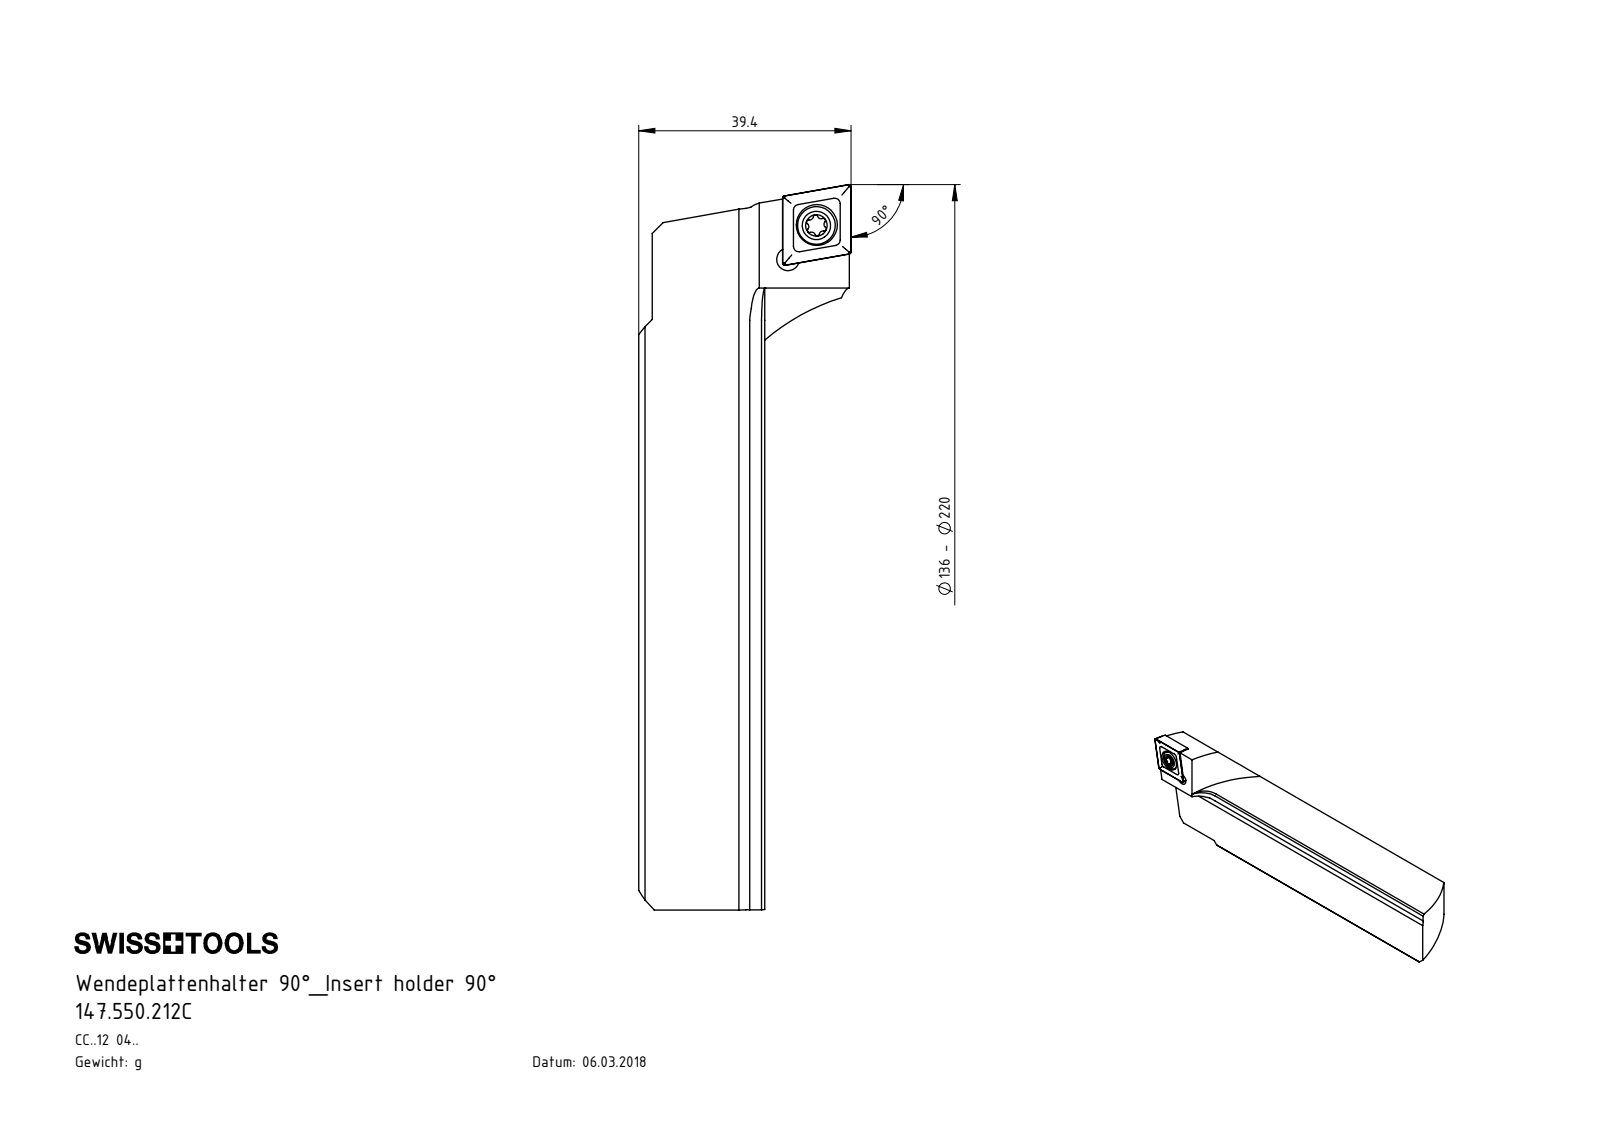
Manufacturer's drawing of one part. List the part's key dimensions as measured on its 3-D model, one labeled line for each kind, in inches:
Part name (STEP PRODUCT): F00-WCC.136.001_C; WCC-ER2.001.010_A; CCMT120404; 147.550.212C
STEP written by: SolidWorks 2017 (CONFIG_CONTROL_DESIGN)
Units: inches
Bodies: 3 solids, 556 faces (342 planar, 40 cylindrical, 174 other)
Overall size (bounding box): 5.299 × 1.551 × 1.077
Volume: 3.406 in³ · Surface area: 22.32 in²
Round holes (diameter × count): ⌀0.165 ×2, ⌀0.217 ×1, ⌀0.299 ×1
Round bosses / shafts (diameter × count): ⌀0.276 ×1, ⌀0.197 ×1
Partial cylindrical surfaces — rounded edges, fillets, slot ends (radius × count): R0.008 ×8, R0.015 ×6, R0.027 ×4, R1.575 ×3, R0.027 ×2, R0.031 ×1, R0.236 ×1
Main face-to-face distances: 0.094, 0.187, 0.839, 0.281, 0.375, 0.188, 0.281, 0.375, 0.469, 0.563
Hole centre spacings: 0.323, 0.328
